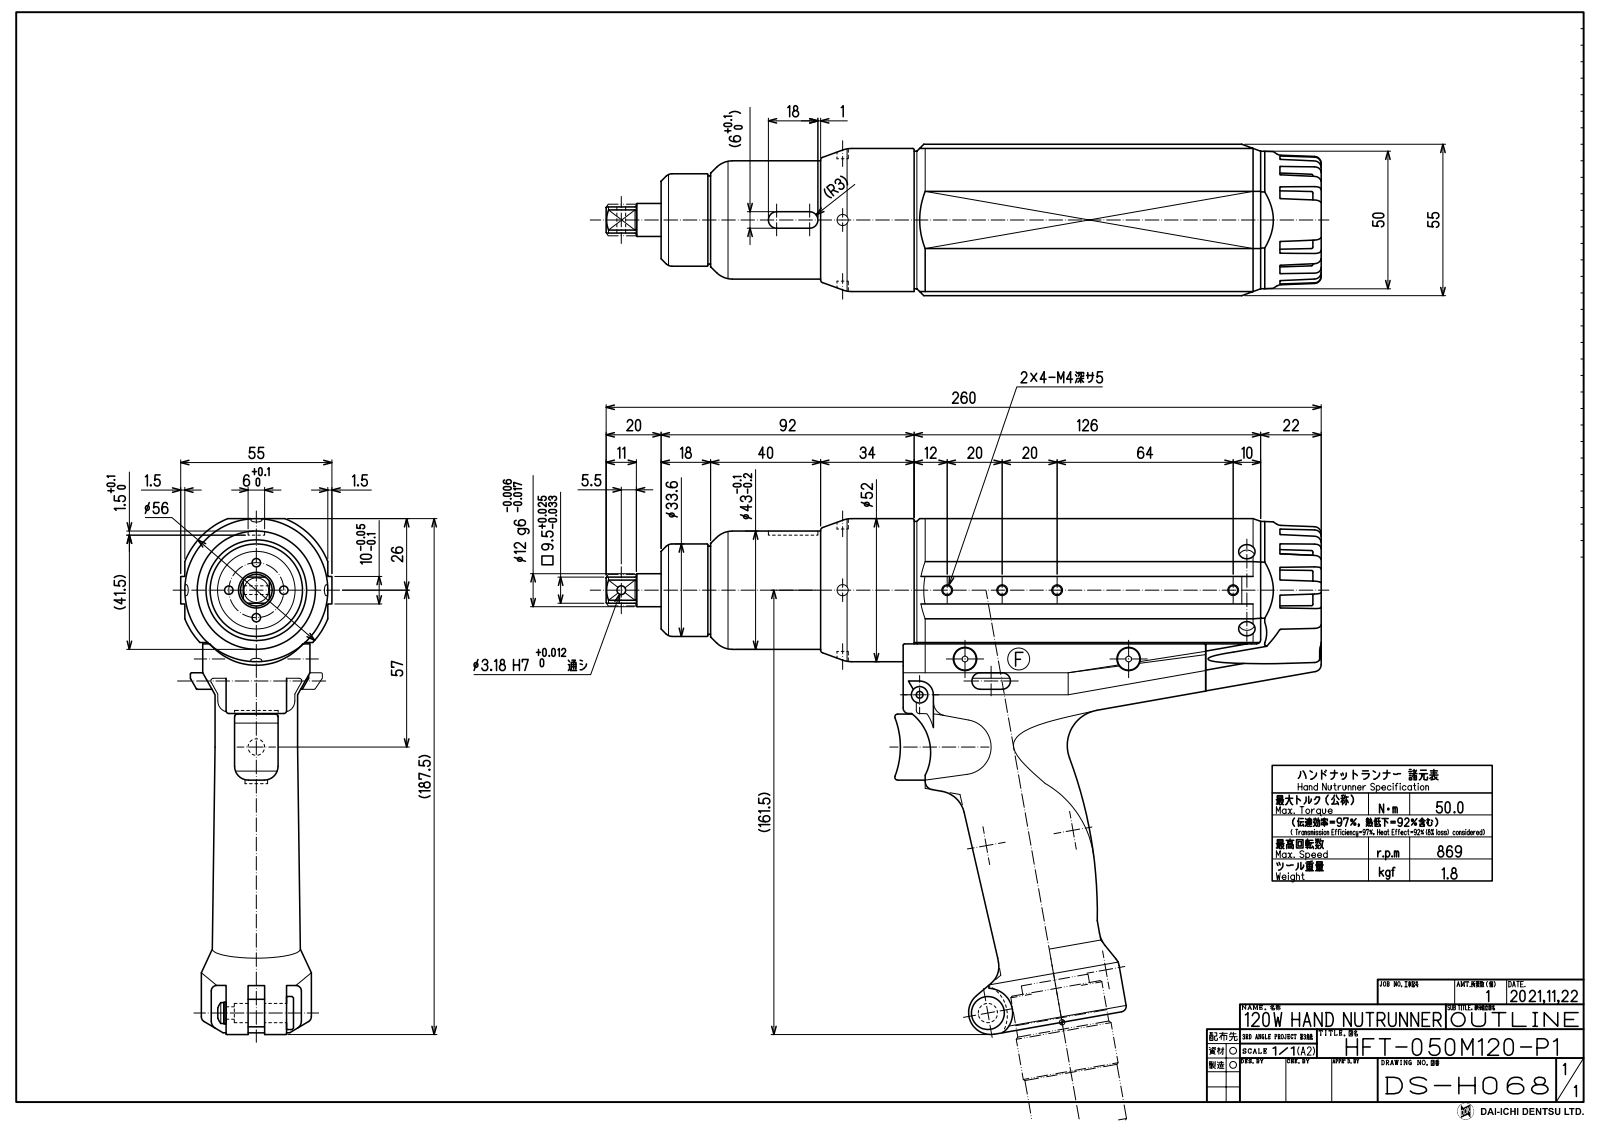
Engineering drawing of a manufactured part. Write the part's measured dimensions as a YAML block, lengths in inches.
part_name: "HFT-030M120-P1(DS-H069)_OUTLINE"
step_written_by: "Autodesk Inventor 2023 (CONFIG_CONTROL_DESIGN)"
units: inches
bodies: {solids: 1, faces: 1477, planar: 629, cylindrical: 288, other: 560}
overall_size: [10.236, 7.38, 2.165]
volume: 40.64
surface_area: 163.6
round_holes:
  - {diameter: 0.128, count: 9}
  - {diameter: 0.236, count: 6}
  - {diameter: 0.097, count: 2}
  - {diameter: 0.161, count: 2}
  - {diameter: 0.335, count: 2}
  - {diameter: 0.098, count: 1}
  - {diameter: 0.125, count: 1}
  - {diameter: 0.177, count: 1}
  - {diameter: 0.228, count: 1}
  - {diameter: 0.315, count: 1}
  - {diameter: 0.89, count: 1}
  - {diameter: 0.984, count: 1}
round_bosses_or_shafts:
  - {diameter: 0.039, count: 24}
  - {diameter: 0.217, count: 5}
  - {diameter: 0.063, count: 4}
  - {diameter: 0.228, count: 3}
  - {diameter: 0.472, count: 2}
  - {diameter: 0.315, count: 2}
  - {diameter: 0.118, count: 2}
  - {diameter: 2.047, count: 1}
partial_cylinders:
  - {radius: 0.02, count: 22}
  - {radius: 0.039, count: 12}
  - {radius: 0.012, count: 7}
  - {radius: 0.118, count: 6}
  - {radius: 0.079, count: 5}
  - {radius: 0.048, count: 4}
  - {radius: 0.197, count: 4}
  - {radius: 0.098, count: 3}
face_to_face_distances: [0.059, 2.106, 1.791, 0.315, 0.138, 0.591, 1.26, 1.85, 0.256, 0.118]
hole_center_spacings: [0.787, 1.575, 0.669, 0.67, 0.919, 1.017, 1.119, 1.61]
